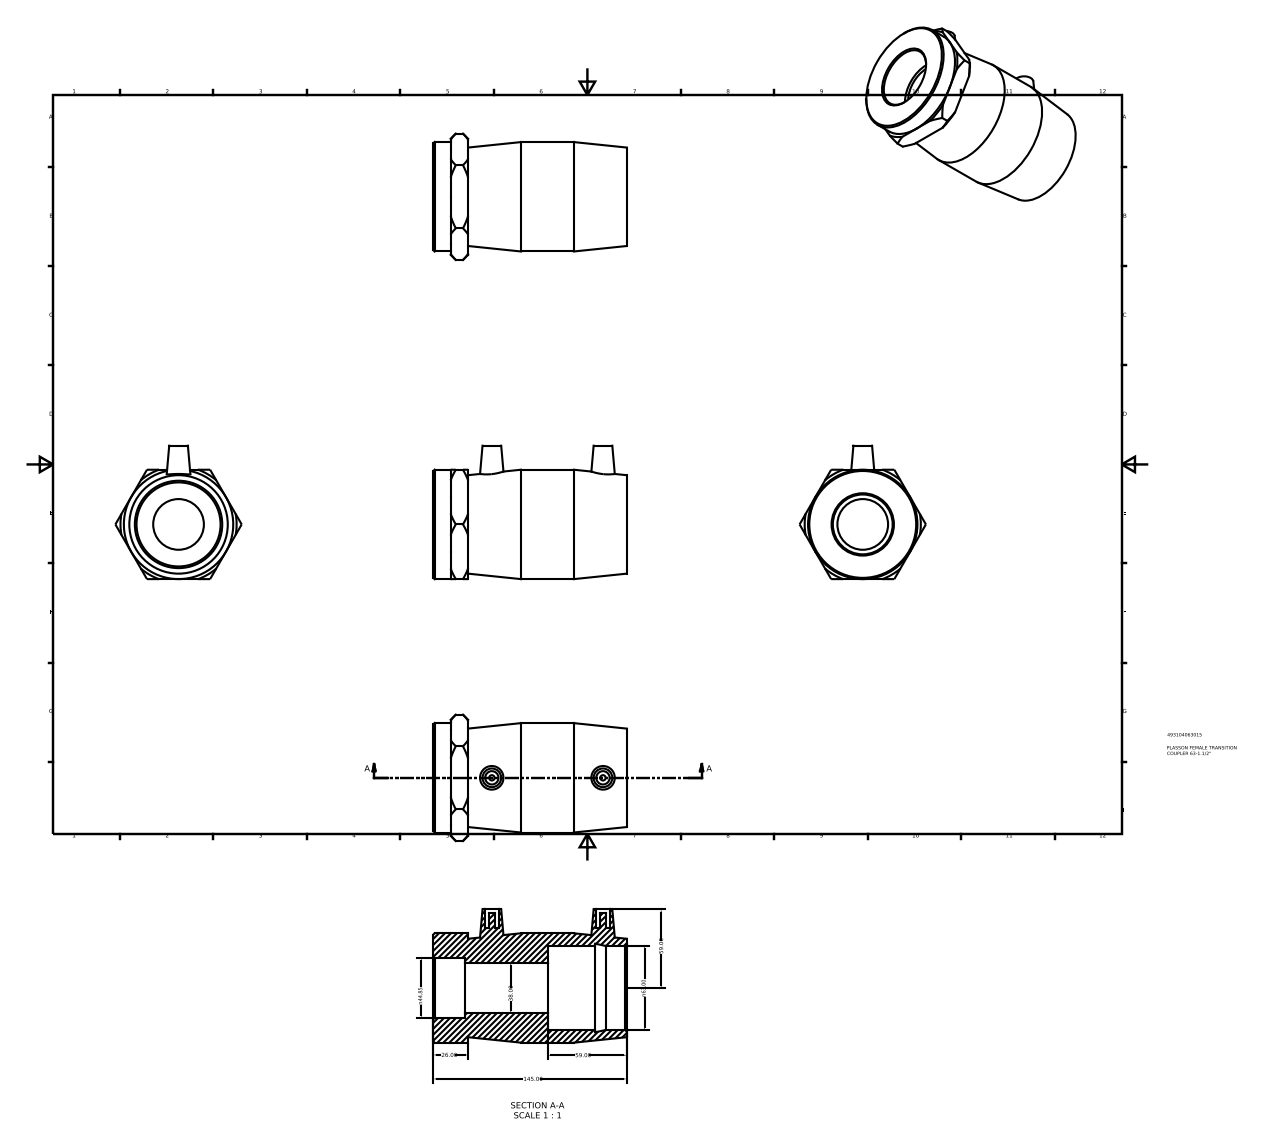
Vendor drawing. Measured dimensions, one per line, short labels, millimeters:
name: 493104063015
written by: Autodesk Inventor 2015 (AP242_MANAGED_MODEL_BASED_3D_ENGINEERING_MIM_LF)
unit: mm
bodies: 1 solid, 54 faces (24 planar, 10 cylindrical, 20 other)
size: 145 × 100 × 94.69
volume: 444 503 mm³; area: 71 452 mm²
holes: 2× ⌀10, 1× ⌀38, 1× ⌀44.84, 1× ⌀63
bosses: 2× ⌀4, 1× ⌀82
face distances: 86, 82, 26, 60, 145, 119, 59, 13, 23.4, 2.6
hole spacings: 83.3
